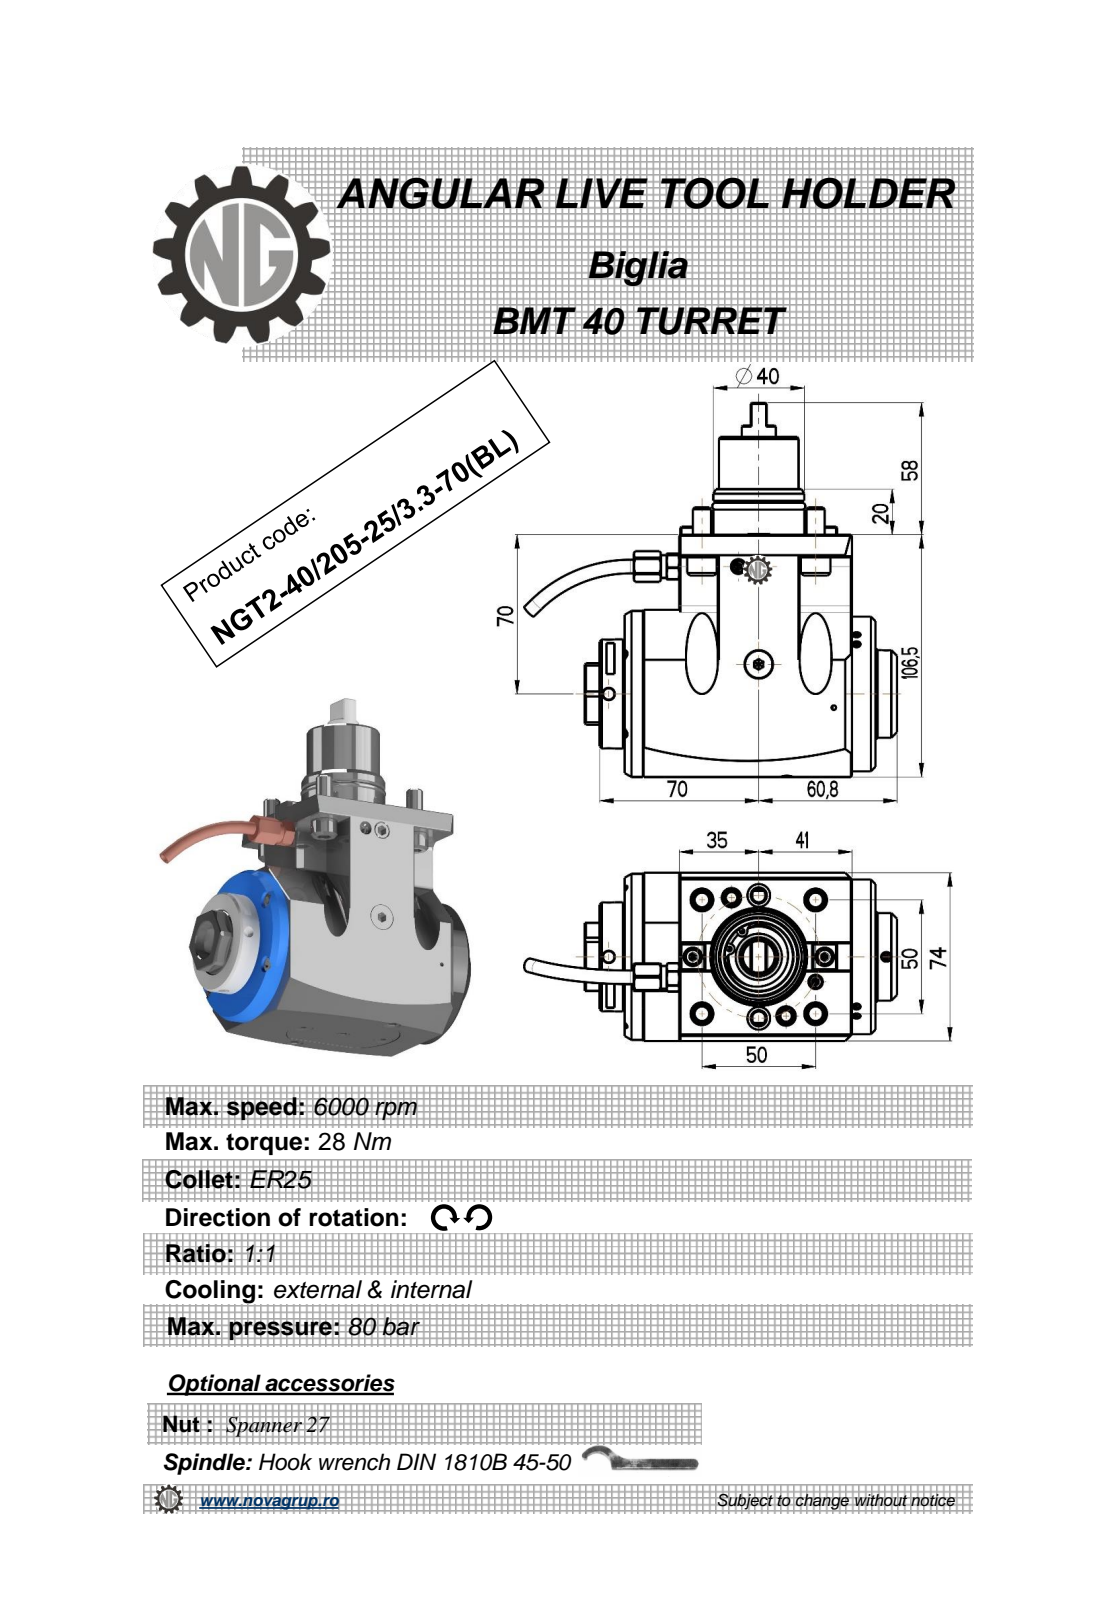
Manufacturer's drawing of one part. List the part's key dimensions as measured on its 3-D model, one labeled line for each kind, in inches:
Part name (STEP PRODUCT): NGT2_40_205_25_3_3_70_BL
STEP written by: PRO/ENGINEER BY PARAMETRIC TECHNOLOGY CORPORATION, 2010280 (CONFIG_CONTROL_DESIGN)
Units: inches
Bodies: 1 solid, 419 faces (195 planar, 120 cylindrical, 104 other)
Overall size (bounding box): 6.476 × 6.456 × 2.913
Volume: 46.37 in³ · Surface area: 107.7 in²
Round holes (diameter × count): ⌀0.157 ×2, ⌀0.197 ×2, ⌀0.236 ×2, ⌀0.709 ×1, ⌀1.043 ×1
Round bosses / shafts (diameter × count): ⌀0.512 ×4, ⌀0.315 ×4, ⌀0.236 ×2, ⌀2.874 ×1, ⌀2.677 ×1, ⌀1.89 ×1, ⌀1.575 ×1, ⌀1.516 ×1
Partial cylindrical surfaces — rounded edges, fillets, slot ends (radius × count): R0.01 ×20, R0.157 ×4, R0.276 ×4, R0.031 ×2, R9.843 ×2, R0.246 ×1, R0.266 ×1, R0.591 ×1
Main face-to-face distances: 2.913, 4.193, 2.047, 2.087, 0.906, 3.937, 4.343, 0.406, 2.992, 2.323
Hole centre spacings: 2.807, 2.126, 2.233
